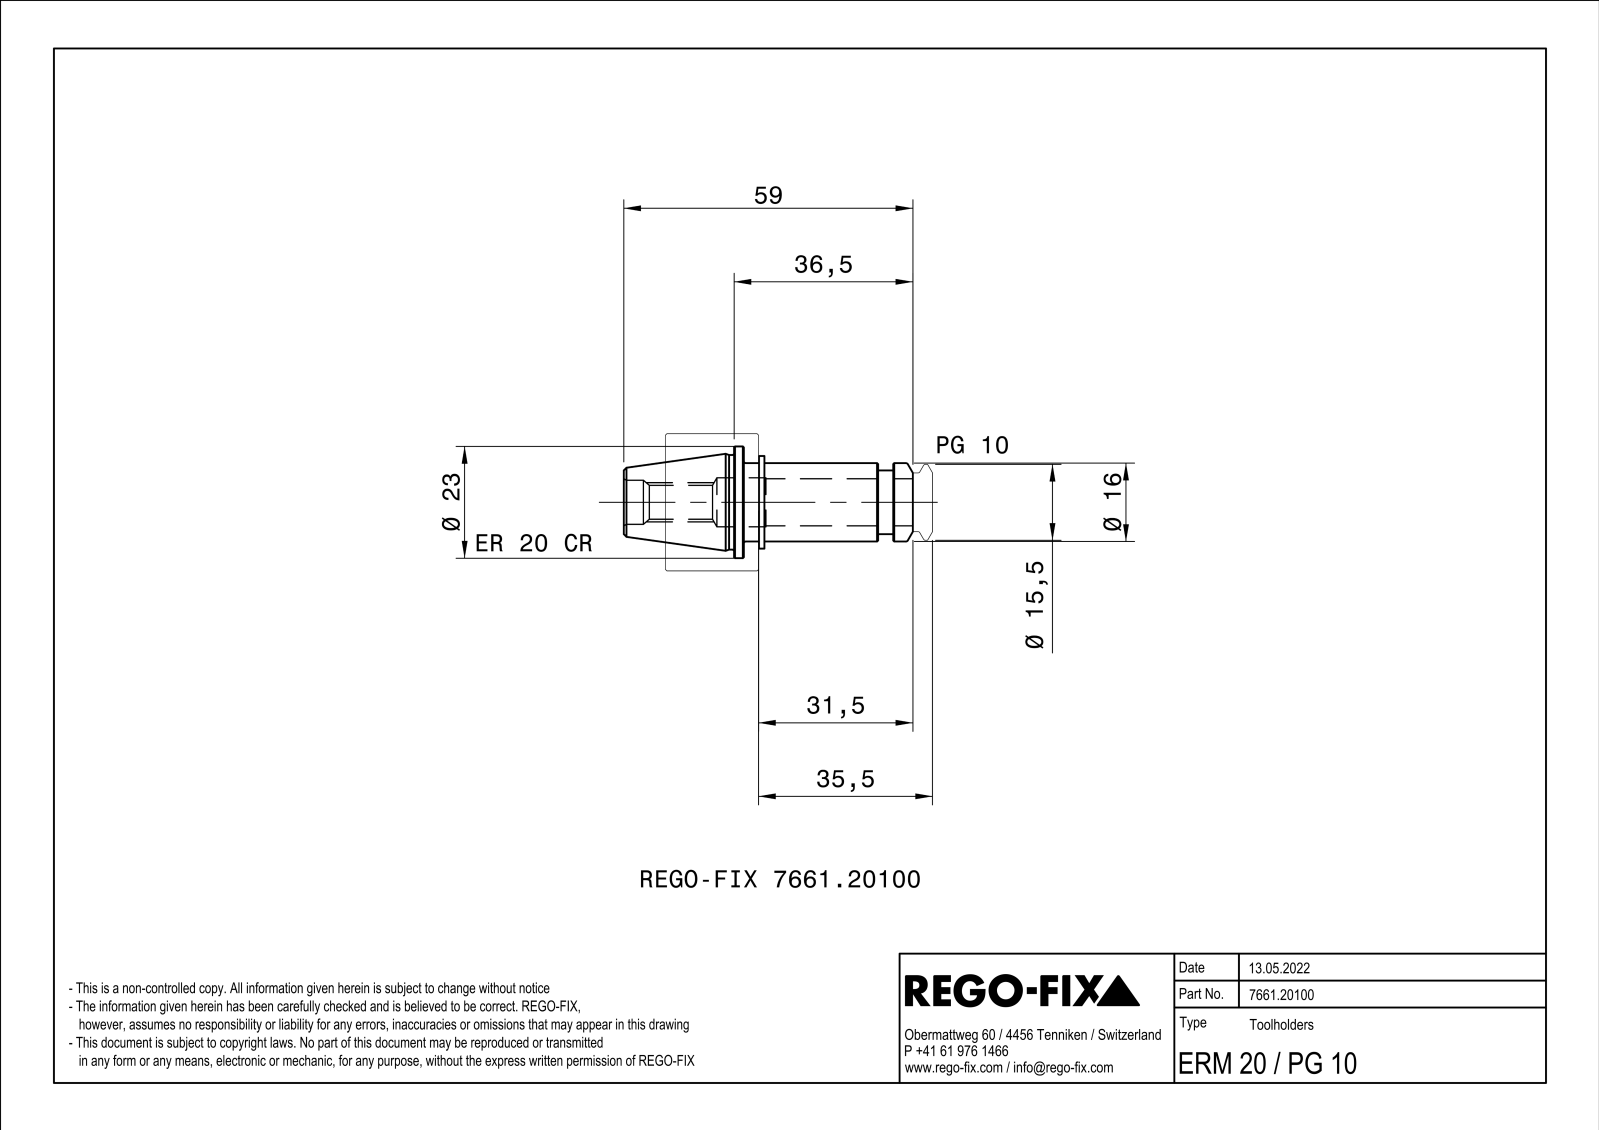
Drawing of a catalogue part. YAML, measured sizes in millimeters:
part_name: "NOCUT"
step_written_by: "SIEMENS PLM Software Solid Edge ST10 (AUTOMOTIVE_DESIGN)"
units: millimeters
bodies: {solids: 1, faces: 78, planar: 34, cylindrical: 15, other: 29}
overall_size: [59, 28, 28]
volume: 11496
surface_area: 8080
round_holes:
  - {diameter: 6.92, count: 1}
  - {diameter: 8.5, count: 1}
  - {diameter: 10, count: 1}
  - {diameter: 16.4, count: 1}
  - {diameter: 22.92, count: 1}
  - {diameter: 24.3, count: 1}
round_bosses_or_shafts:
  - {diameter: 28, count: 1}
  - {diameter: 22.8, count: 1}
  - {diameter: 19.3, count: 1}
  - {diameter: 18.9, count: 1}
  - {diameter: 16, count: 1}
  - {diameter: 14.3, count: 1}
  - {diameter: 13, count: 1}
face_to_face_distances: [5, 27.5, 12.5, 1.15, 13.65, 1, 12.65, 3.1, 27.4, 1.05]
